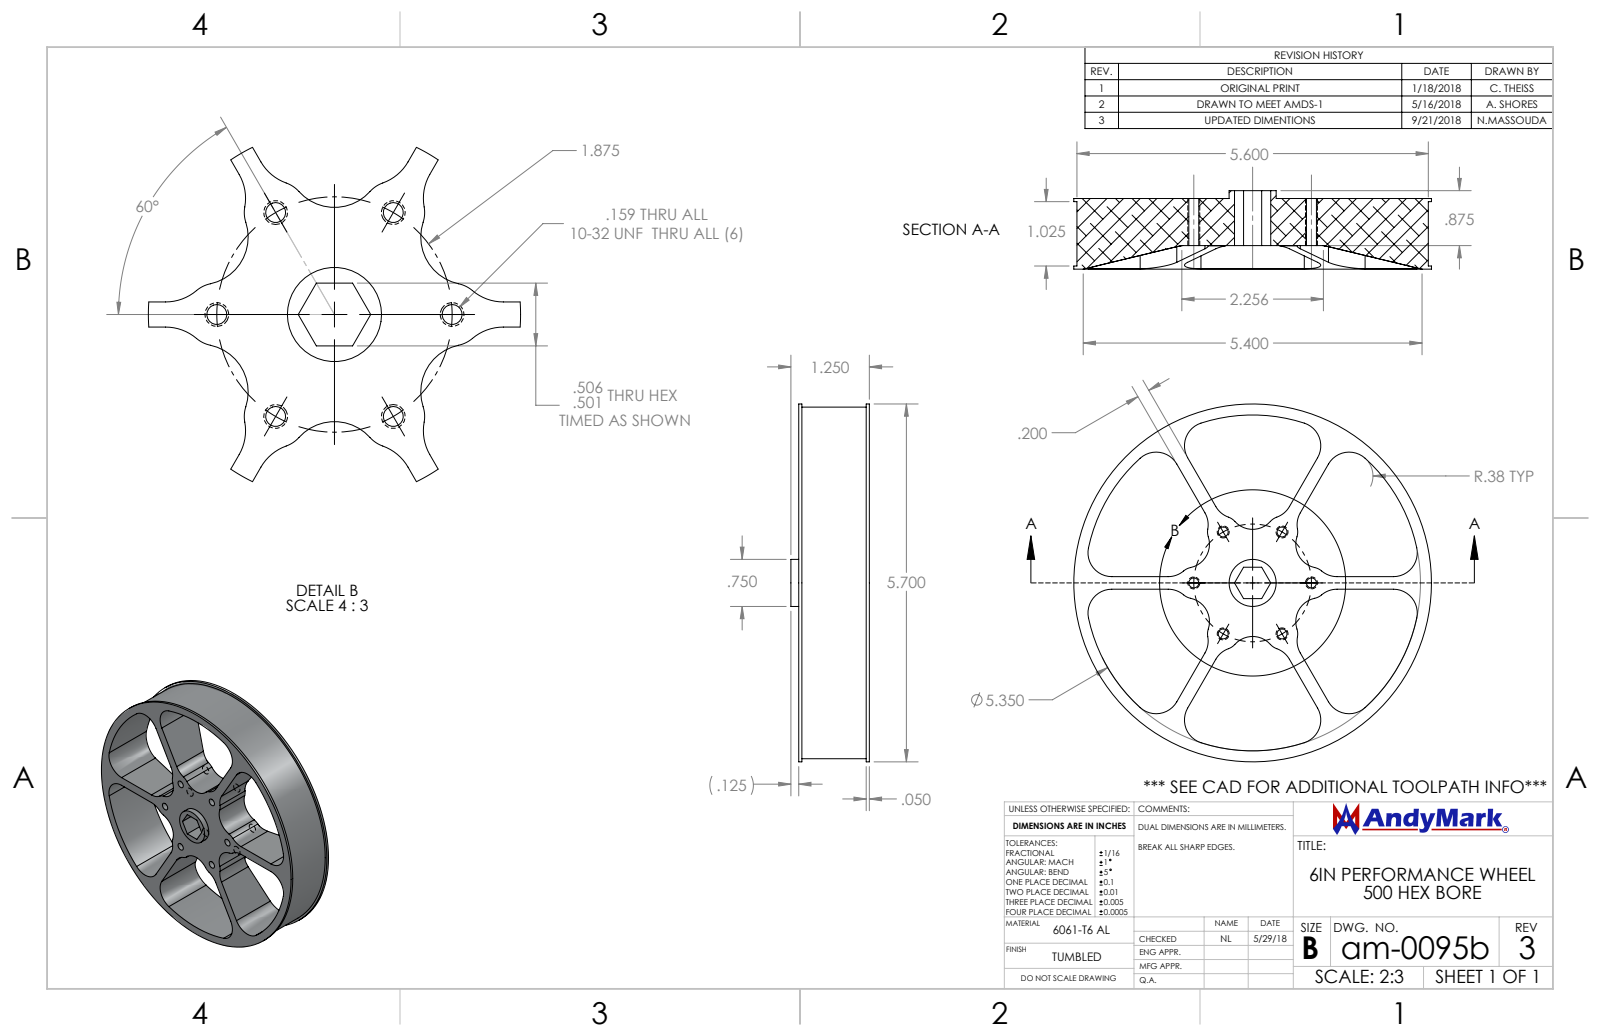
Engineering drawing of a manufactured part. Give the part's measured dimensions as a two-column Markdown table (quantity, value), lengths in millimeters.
| quantity | value |
| --- | --- |
| part name | am-0095b 6in Perf 500 Hex REV3 |
| STEP written by | SolidWorks 2018 (CONFIG_CONTROL_DESIGN) |
| units | millimeters |
| bodies | 1 solid, 111 faces (24 planar, 78 cylindrical, 9 other) |
| overall size | 144.8 × 144.8 × 31.8 |
| volume | 114 900 mm³ |
| surface area | 50 740 mm² |
| round holes (diameter × count) | 4 × 6 |
| round bosses / shafts (diameter × count) | 144.8 × 1, 142.2 × 1, 19.1 × 1 |
| partial cylindrical surfaces (radius × count) | 9.7 × 30, 6.4 × 6, 67.9 × 1 |
| main face-to-face distances | 5.1, 19.1, 9.5, 28.6, 1.3, 27.3, 3.8, 8.9, 8.3, 26 |
| hole center spacings | 41.2, 23.8, 47.6, 23.8 |
